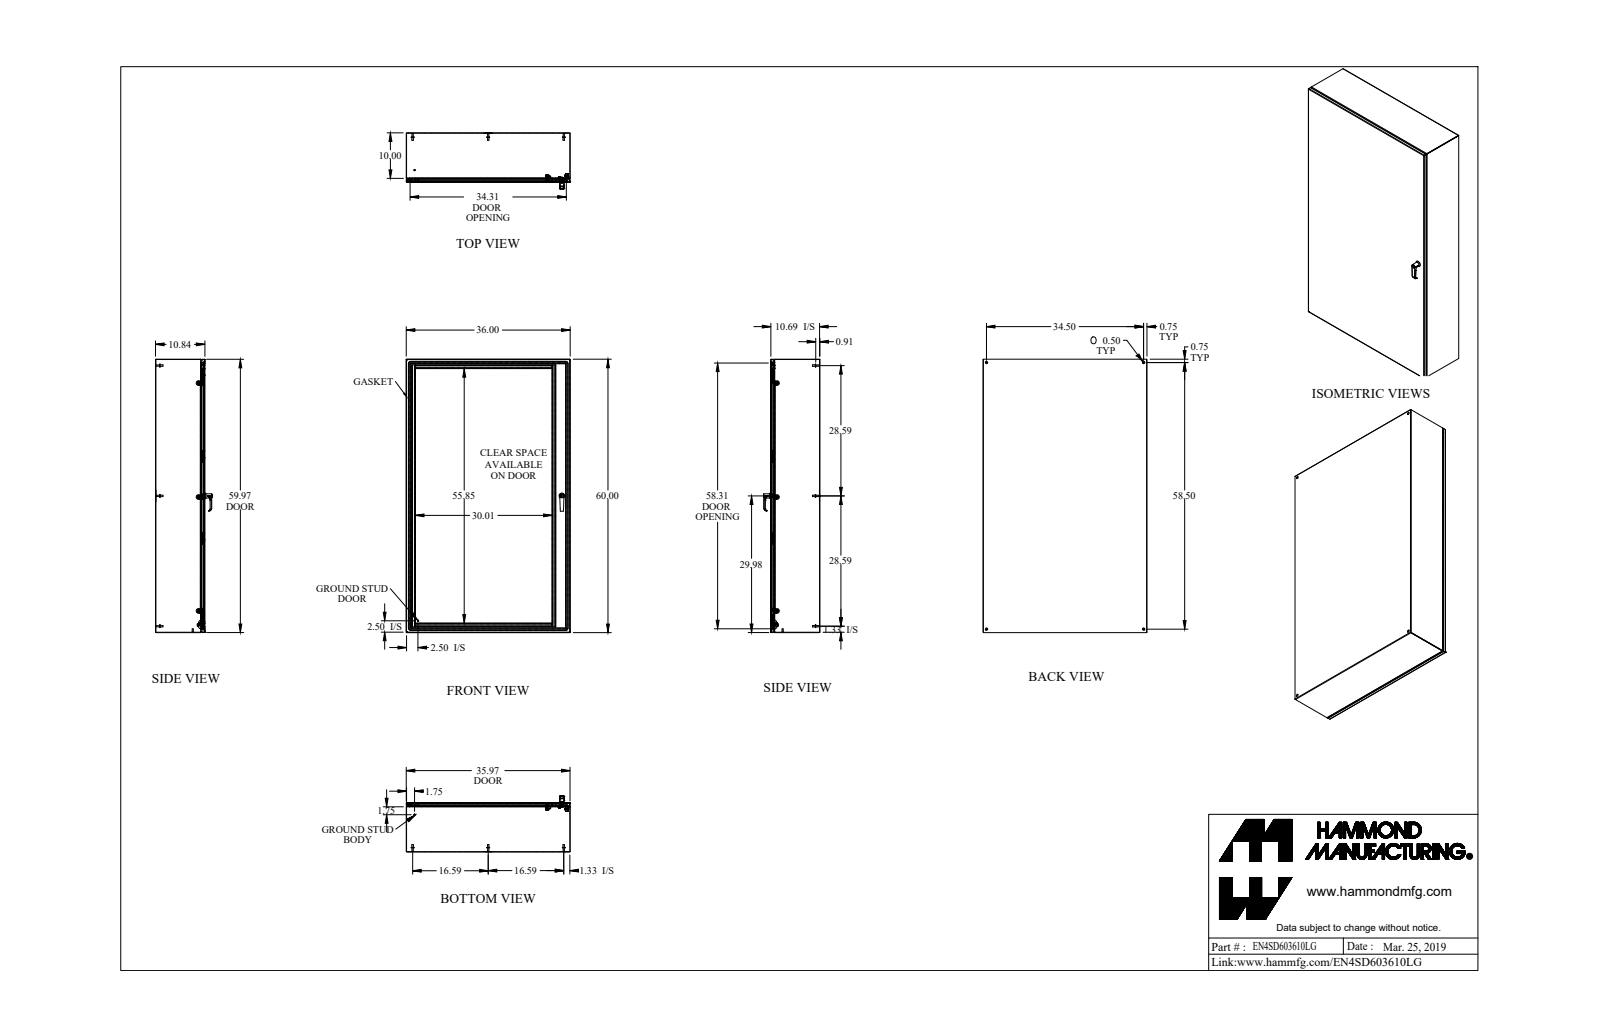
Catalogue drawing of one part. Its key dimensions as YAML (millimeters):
part_name: "EN4SD603610LG"
step_written_by: "SolidWorks 2018 (AUTOMOTIVE_DESIGN)"
units: millimeters
bodies: {solids: 63, faces: 1711, planar: 757, cylindrical: 632, other: 322}
overall_size: [1524, 914.4, 314.1]
volume: 8598000
surface_area: 9556000
round_holes:
  - {diameter: 4.5, count: 6}
  - {diameter: 5, count: 4}
  - {diameter: 12.7, count: 4}
  - {diameter: 6.4, count: 3}
  - {diameter: 6.7, count: 3}
  - {diameter: 10.5, count: 3}
  - {diameter: 6.5, count: 2}
  - {diameter: 8, count: 2}
  - {diameter: 10, count: 2}
  - {diameter: 4.4, count: 1}
  - {diameter: 6.1, count: 1}
  - {diameter: 6.1, count: 1}
round_bosses_or_shafts:
  - {diameter: 8, count: 8}
  - {diameter: 6.9, count: 8}
  - {diameter: 6.4, count: 7}
  - {diameter: 15.9, count: 6}
  - {diameter: 9.5, count: 6}
  - {diameter: 4, count: 6}
  - {diameter: 25.4, count: 3}
  - {diameter: 15.9, count: 3}
partial_cylinders:
  - {radius: 1.1, count: 24}
  - {radius: 0.9, count: 18}
  - {radius: 1.6, count: 18}
  - {radius: 2.7, count: 18}
  - {radius: 0.8, count: 15}
  - {radius: 2.4, count: 10}
  - {radius: 0.4, count: 9}
  - {radius: 0.2, count: 8}
face_to_face_distances: [1.8, 273.4, 271.6, 275.3, 912.6, 910.7, 914.4, 1.8, 1520.3, 1522.2]
hole_center_spacings: [635, 876.3, 1270, 1485.9, 1725, 19.7, 20, 20.3]
